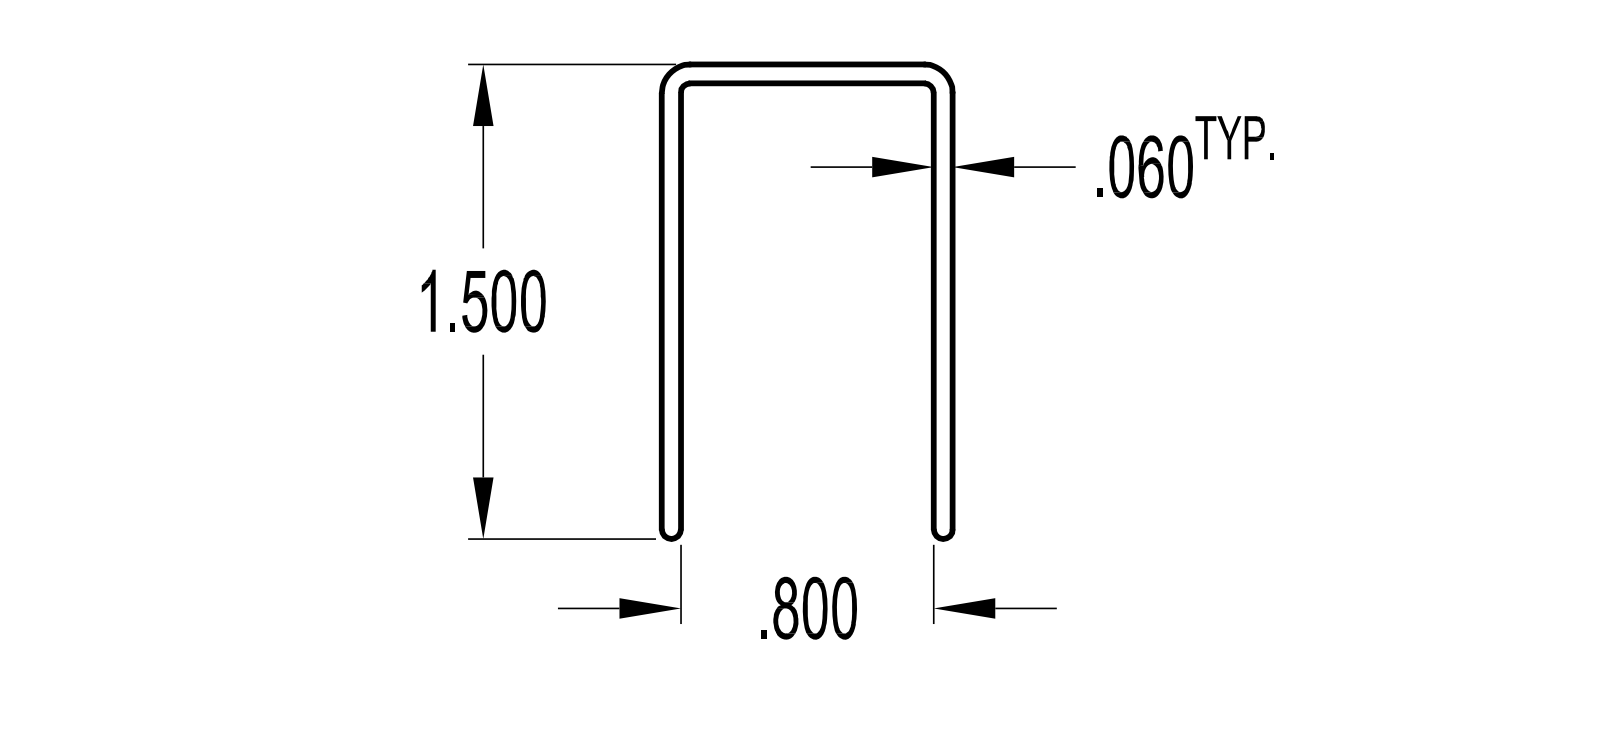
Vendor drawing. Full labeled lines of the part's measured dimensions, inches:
STEP written by: KeyCreator Pro (AUTOMOTIVE_DESIGN)
Units: inches
Bodies: 1 solid, 14 faces (8 planar, 6 cylindrical, 0 other)
Overall size (bounding box): 6 × 1.5 × 0.92
Volume: 1.343 in³ · Surface area: 45.83 in²
Partial cylindrical surfaces — rounded edges, fillets, slot ends (radius × count): R0.03 ×4, R0.093 ×2
Main face-to-face distances: 0.06, 0.8, 0.06, 0.86, 0.92, 0.86, 6
